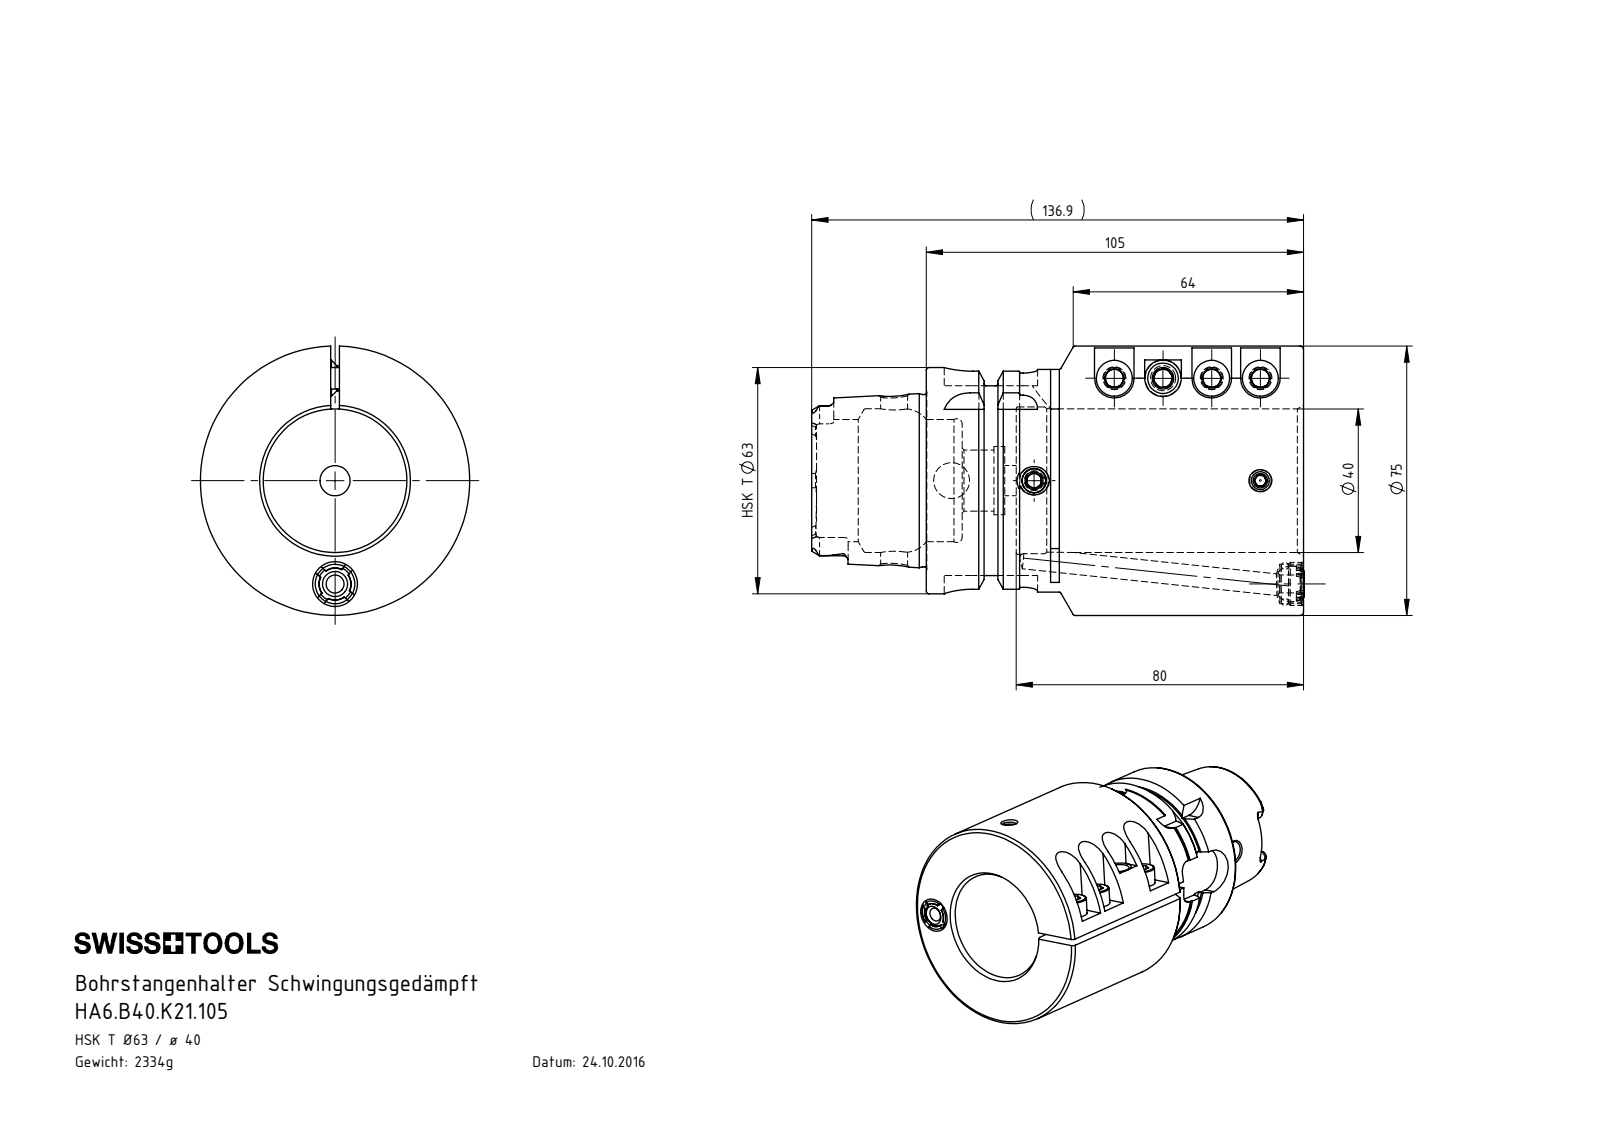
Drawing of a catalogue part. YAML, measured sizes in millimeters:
part_name: "KU1-U12.002.010; HA6.B40.K21.105; ISO 4028 - M10 x 16; ISO 4027 - M6 x 16_PreviewCfg (+6 more)"
step_written_by: "SolidWorks 2017 (AUTOMOTIVE_DESIGN)"
units: millimeters
bodies: {solids: 10, faces: 591, planar: 180, cylindrical: 210, other: 201}
overall_size: [137.38, 75, 74.98]
volume: 297082
surface_area: 65049
round_holes:
  - {diameter: 5, count: 5}
  - {diameter: 6.4, count: 3}
  - {diameter: 10, count: 2}
  - {diameter: 6, count: 1}
  - {diameter: 6.8, count: 1}
  - {diameter: 7.5, count: 1}
  - {diameter: 8.4, count: 1}
  - {diameter: 8.5, count: 1}
  - {diameter: 11, count: 1}
  - {diameter: 17, count: 1}
  - {diameter: 19, count: 1}
  - {diameter: 34, count: 1}
round_bosses_or_shafts:
  - {diameter: 10, count: 4}
  - {diameter: 6, count: 4}
  - {diameter: 75, count: 1}
  - {diameter: 63, count: 1}
  - {diameter: 62, count: 1}
  - {diameter: 54.95, count: 1}
  - {diameter: 47.94, count: 1}
  - {diameter: 12, count: 1}
partial_cylinders:
  - {radius: 1.4, count: 6}
  - {radius: 4, count: 5}
  - {radius: 2.88, count: 4}
  - {radius: 8, count: 4}
  - {radius: 5.5, count: 3}
  - {radius: 62.5, count: 2}
  - {radius: 4.4, count: 1}
  - {radius: 5.1, count: 1}
face_to_face_distances: [2.4, 80, 25, 105, 12, 34.6, 9.6, 70.4, 37, 68]
hole_center_spacings: [13.56, 27.11, 13.55, 23, 28.5, 28.75, 31.56, 36.21]
